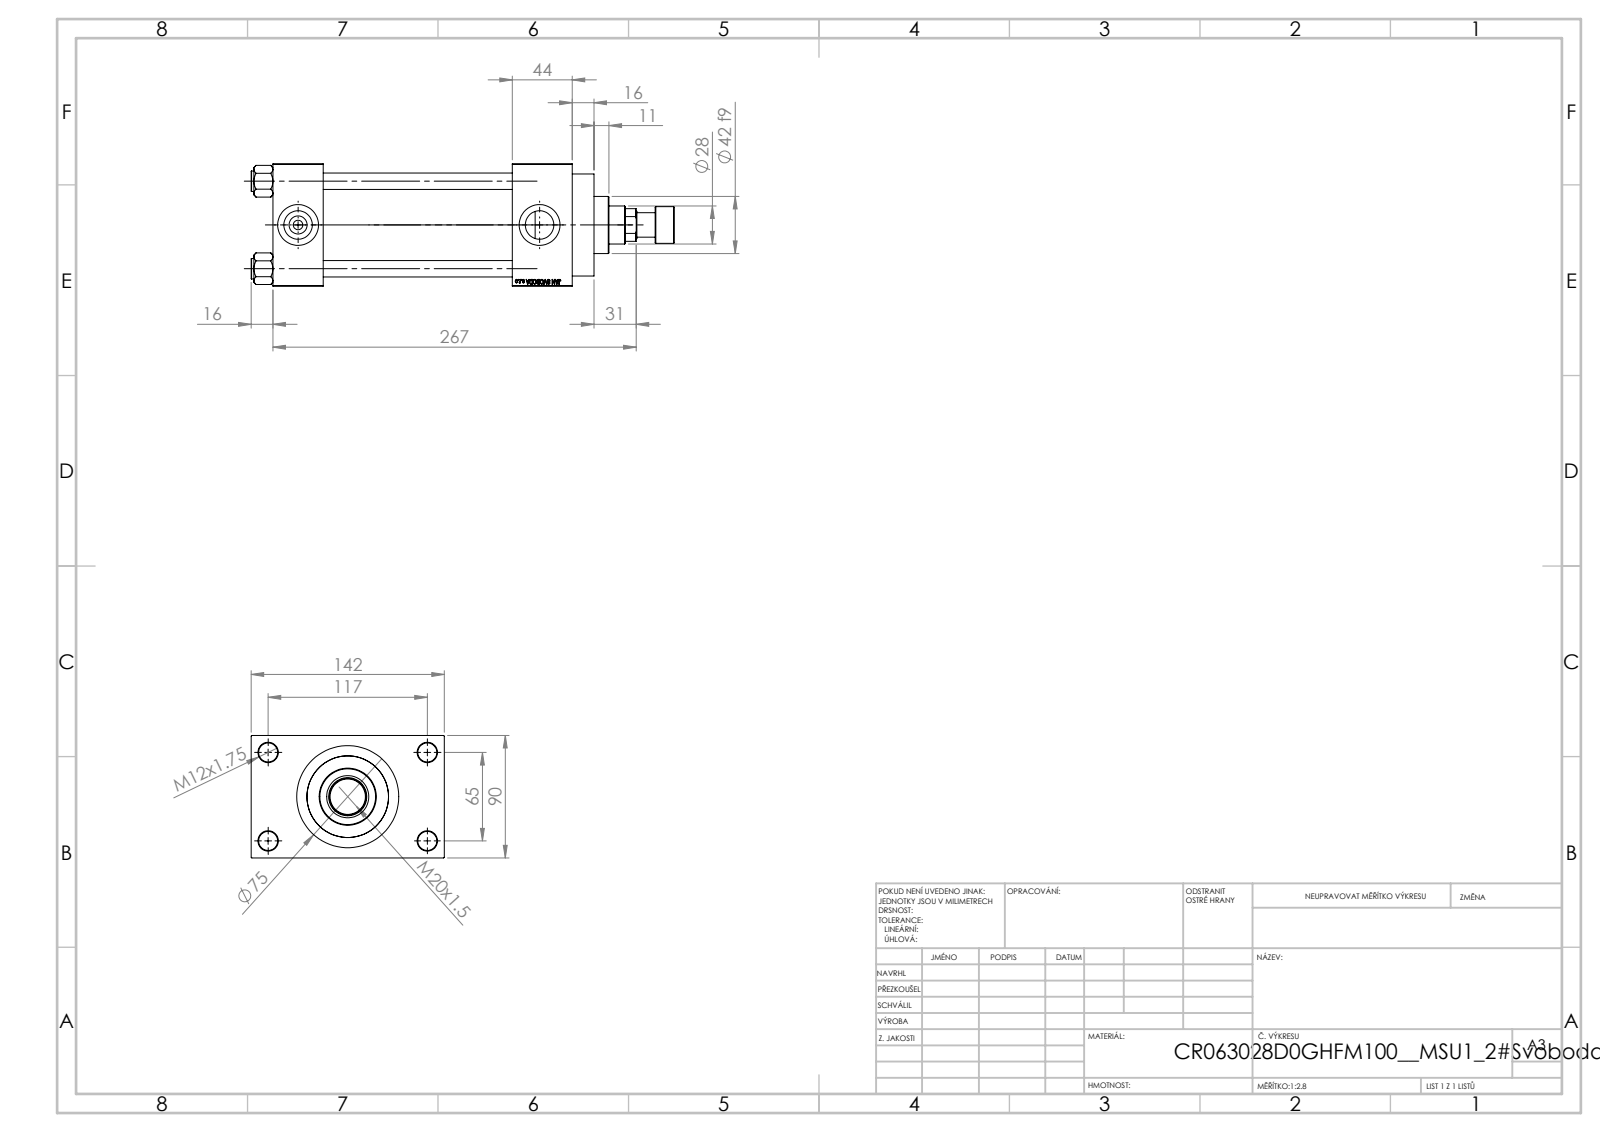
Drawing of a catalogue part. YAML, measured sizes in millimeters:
part_name: "V215CR_ROD_END_F; V215CR_VCP_D; V215CR_D_Body; V215_VC_A (+2 more)"
step_written_by: "SolidWorks 2019 (CONFIG_CONTROL_DESIGN)"
units: millimeters
bodies: {solids: 12, faces: 1117, planar: 501, cylindrical: 92, other: 524}
overall_size: [311, 142, 90]
volume: 1243000
surface_area: 255846
round_holes:
  - {diameter: 12, count: 4}
  - {diameter: 14, count: 4}
  - {diameter: 7, count: 2}
  - {diameter: 20.96, count: 2}
  - {diameter: 30, count: 2}
  - {diameter: 18.5, count: 1}
  - {diameter: 28, count: 1}
  - {diameter: 31, count: 1}
  - {diameter: 50, count: 1}
  - {diameter: 60, count: 1}
  - {diameter: 63, count: 1}
round_bosses_or_shafts:
  - {diameter: 15, count: 4}
  - {diameter: 75, count: 1}
  - {diameter: 69, count: 1}
  - {diameter: 42, count: 1}
  - {diameter: 27, count: 1}
  - {diameter: 18, count: 1}
face_to_face_distances: [90, 139, 37, 176, 183, 220, 44, 26, 116, 16]
hole_center_spacings: [26.35, 45.47, 64.3, 66.92, 69.81, 90.65, 111.34, 65]
